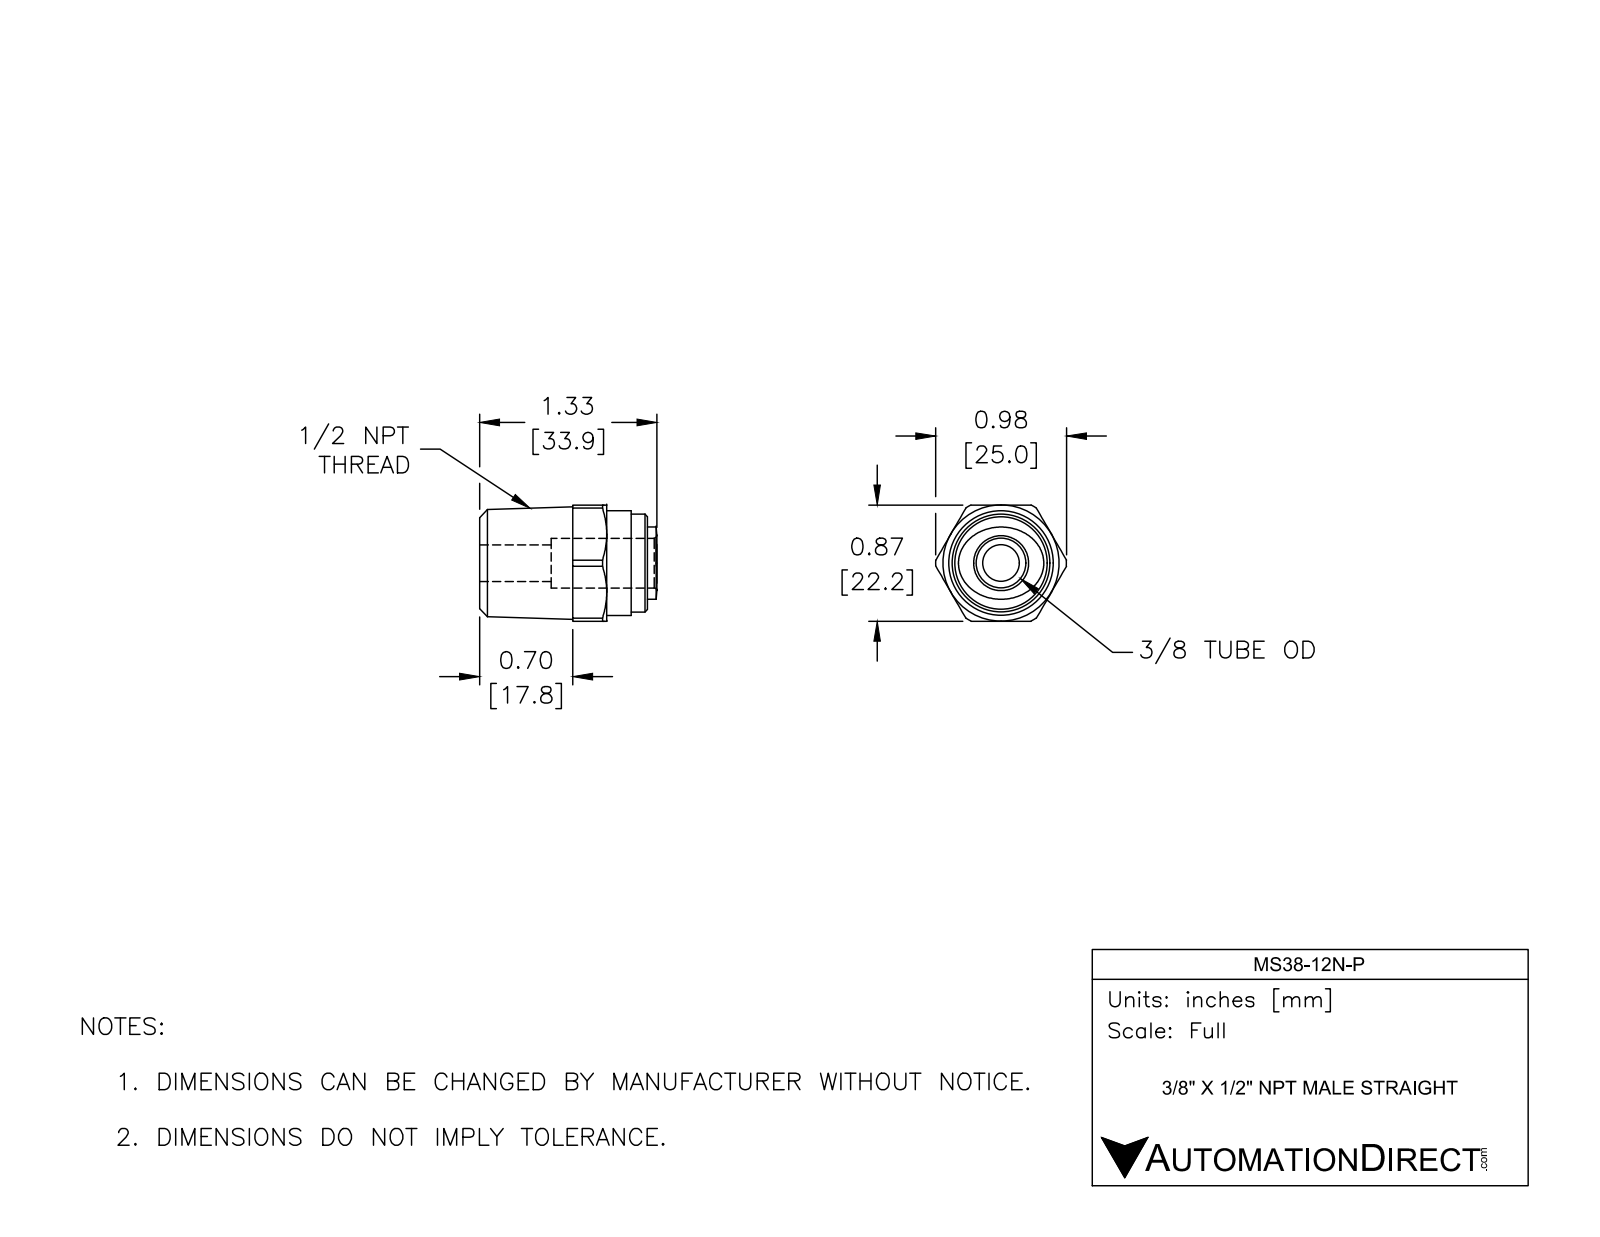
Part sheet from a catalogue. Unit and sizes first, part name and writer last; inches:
Units: inches
Overall size (bounding box): 1.335 × 0.984 × 0.874
Round holes (diameter × count): ⌀0.276 ×1, ⌀0.374 ×1
Round bosses / shafts (diameter × count): ⌀0.787 ×1, ⌀0.736 ×1
Partial cylindrical surfaces — rounded edges, fillets, slot ends (radius × count): R0.492 ×1
Main face-to-face distances: 0.874, 0.957, 1.264, 0.307, 0.701, 0.256, 0.563, 1.142, 0.441, 0.185
Volume: 0.579 in³ · Surface area: 5.832 in²
Bodies: 1 solid, 45 faces (12 planar, 15 cylindrical, 18 other)
Part name (STEP PRODUCT): MS38-12N-P
STEP written by: SolidWorks 2017 (AUTOMOTIVE_DESIGN)
